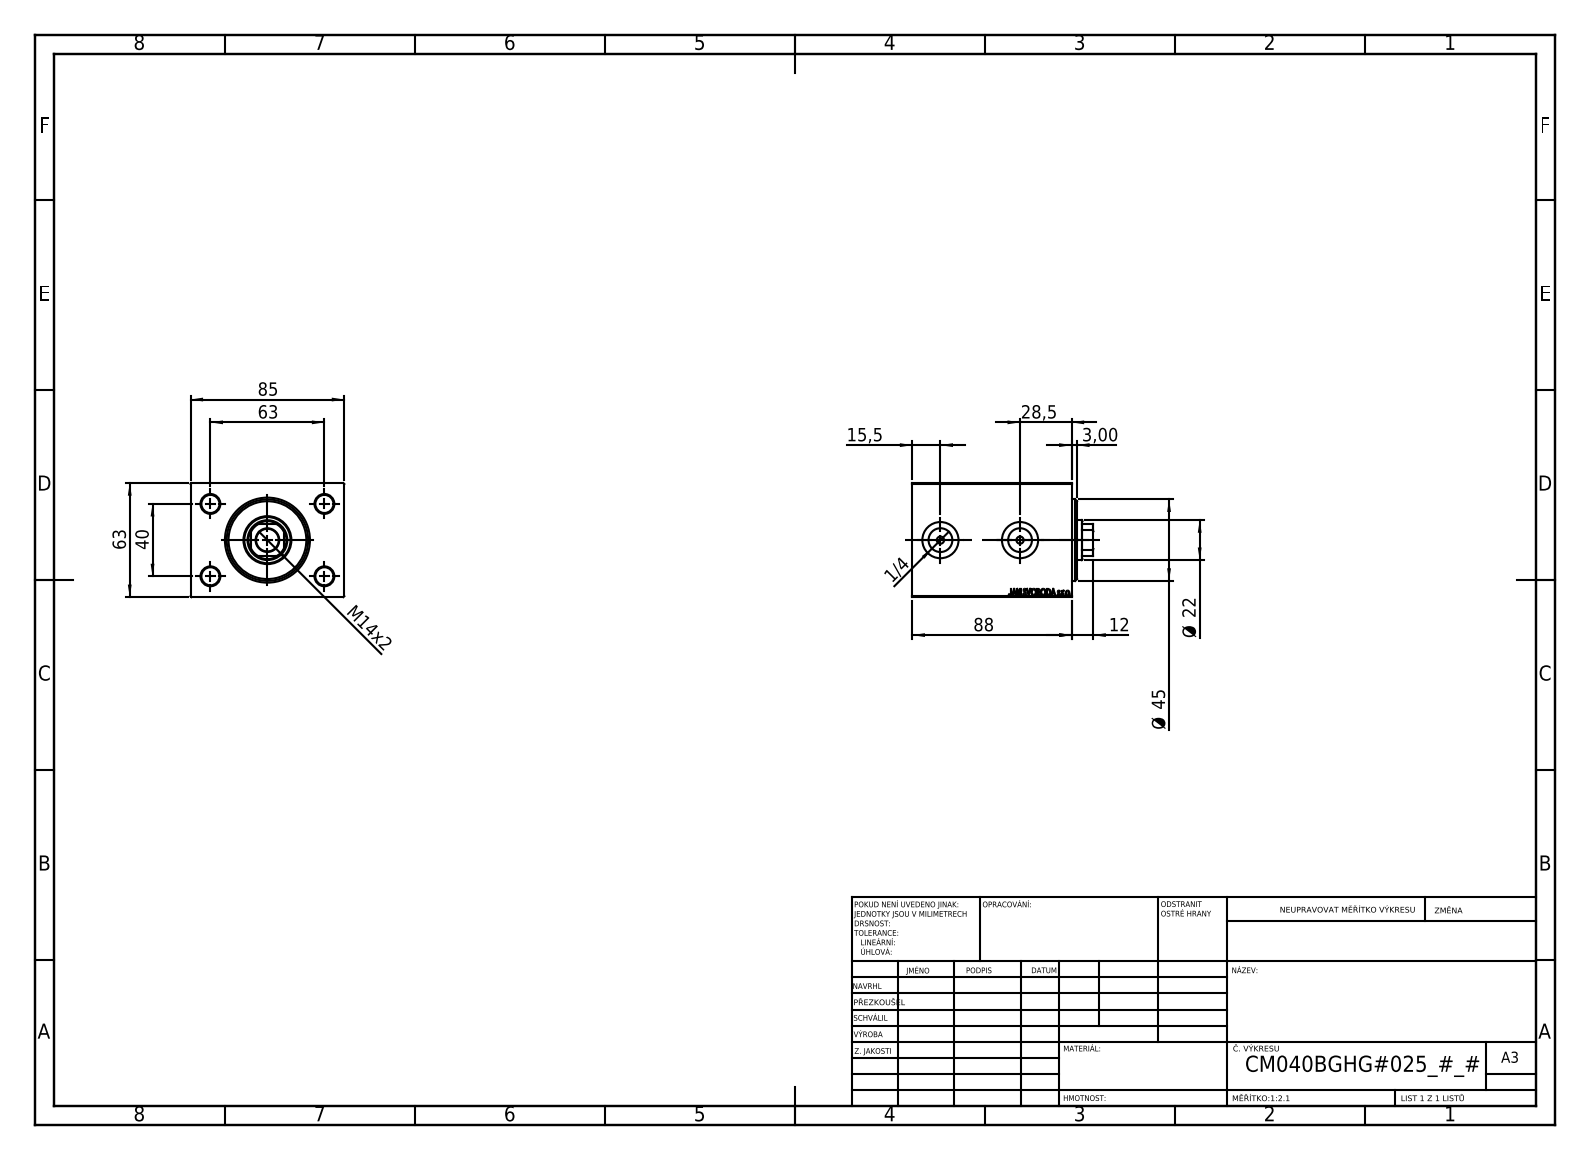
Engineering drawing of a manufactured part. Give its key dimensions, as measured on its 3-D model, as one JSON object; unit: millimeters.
{"part_name": "V450CM_VC_B; V450CM_B_Body; V450CM_B_VCP", "step_written_by": "SolidWorks 2019 (CONFIG_CONTROL_DESIGN)", "units": "millimeters", "bodies": {"solids": 3, "faces": 881, "planar": 401, "cylindrical": 54, "other": 426}, "overall_size": [100, 85, 63], "volume_mm3": 437094, "surface_area_mm2": 69675, "round_holes": [[10, 4], [4, 2], [13.16, 2], [20, 2], [12.5, 1], [22, 1], [25.5, 1], [26.5, 1], [40, 1], [42, 1], [45, 1]], "partial_cylinders_radius": [[10.5, 1]], "face_to_face_distances": [63, 85, 12, 76, 88, 64, 3, 15, 79, 91], "hole_center_spacings": [37.31, 40, 63, 74.63, 44]}
